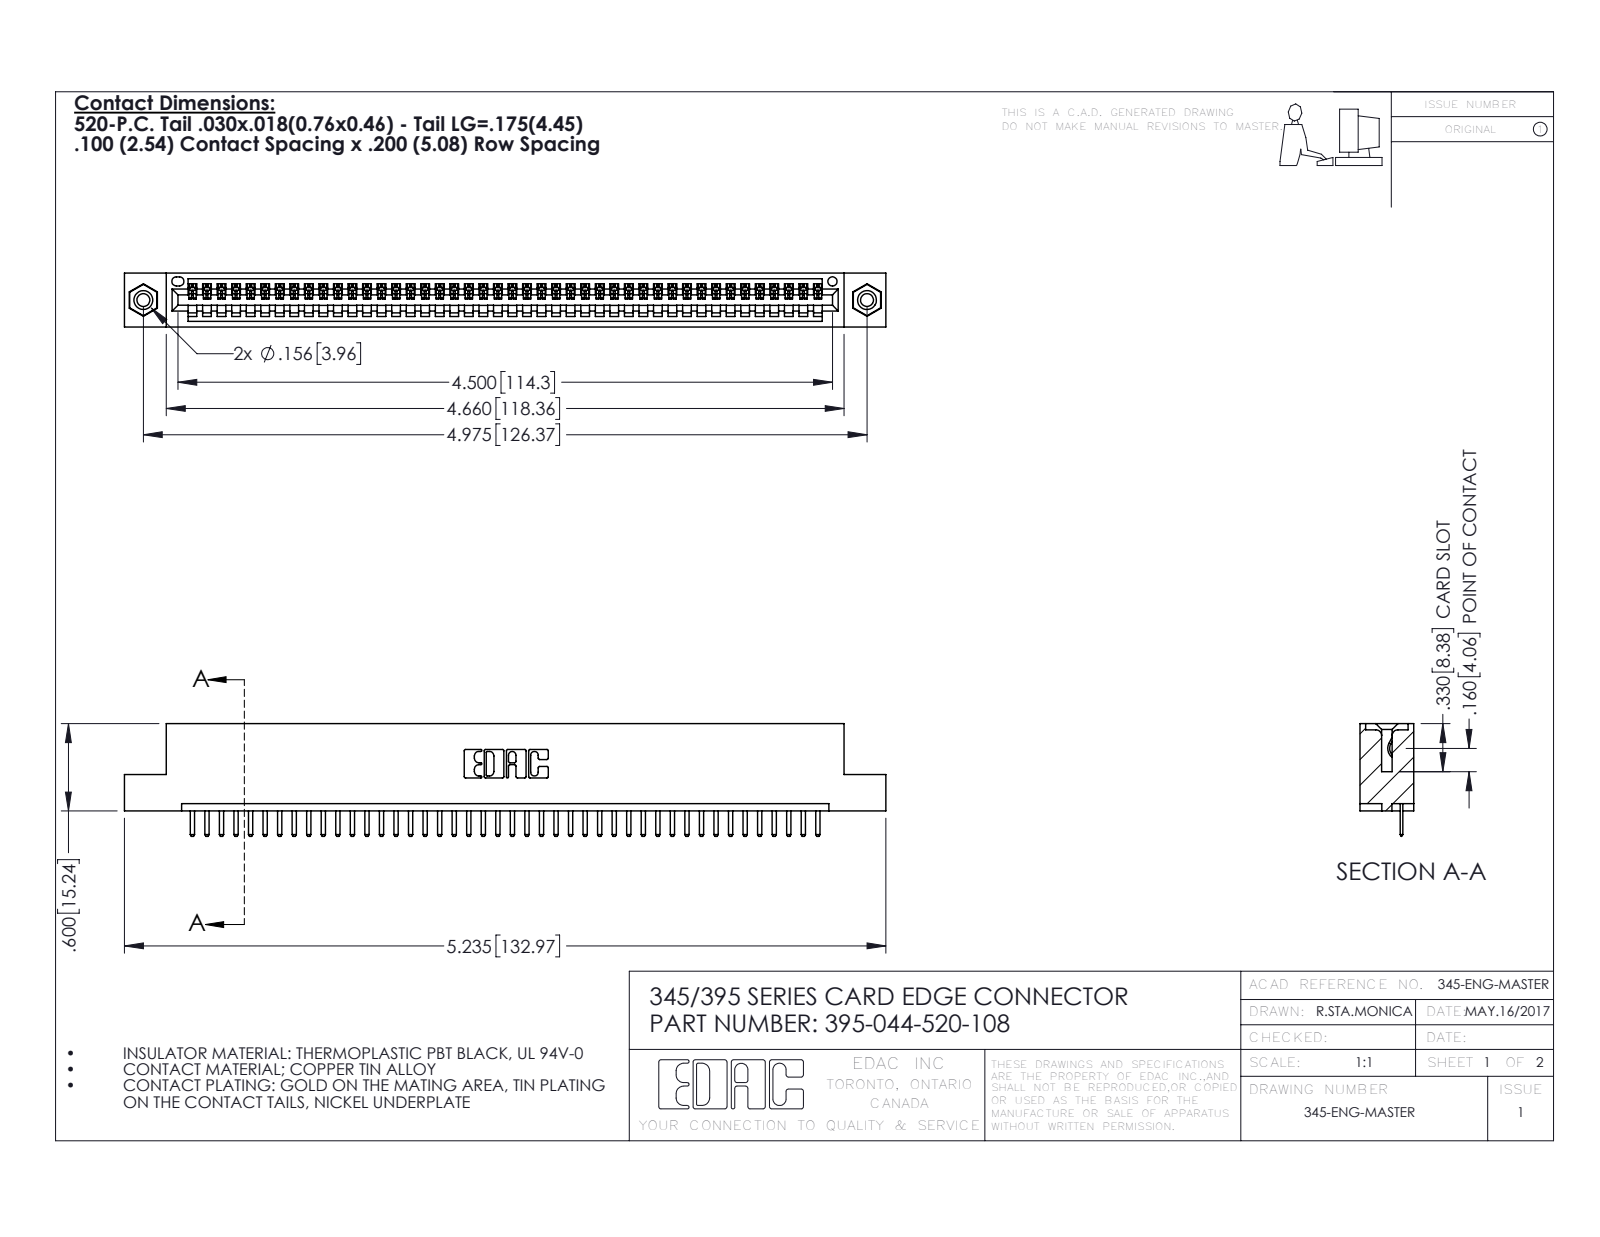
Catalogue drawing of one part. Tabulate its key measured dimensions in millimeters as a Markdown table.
| quantity | value |
| --- | --- |
| part name | 345-250-001_345-250-003-102; 345-292-001_345-293-120; 345 Part_Flush Mounting Lugs - 0.156 Dia-TI; 395-044-520-108 |
| STEP written by | SolidWorks 2016 (CONFIG_CONTROL_DESIGN) |
| units | millimeters |
| bodies | 47 solids, 2914 faces (1960 planar, 938 cylindrical, 16 other) |
| overall size | 133 × 19.7 × 9.4 |
| volume | 12 500 mm³ |
| surface area | 16 260 mm² |
| round holes (diameter × count) | 2.3 × 2, 3.2 × 2, 4 × 2, 1.6 × 1 |
| round bosses / shafts (diameter × count) | 3.9 × 2 |
| partial cylindrical surfaces (radius × count) | 0.3 × 90, 0.2 × 88, 0.3 × 22, 0.2 × 6, 0.8 × 6, 0.7 × 3, 0.8 × 2, 1 × 2 |
| main face-to-face distances | 1.8, 7.6, 9.4, 5.1, 2.5, 6.9, 0.6, 5.7, 1.8, 3.8 |
| hole center spacings | 6.9, 120.4, 126.4 |
